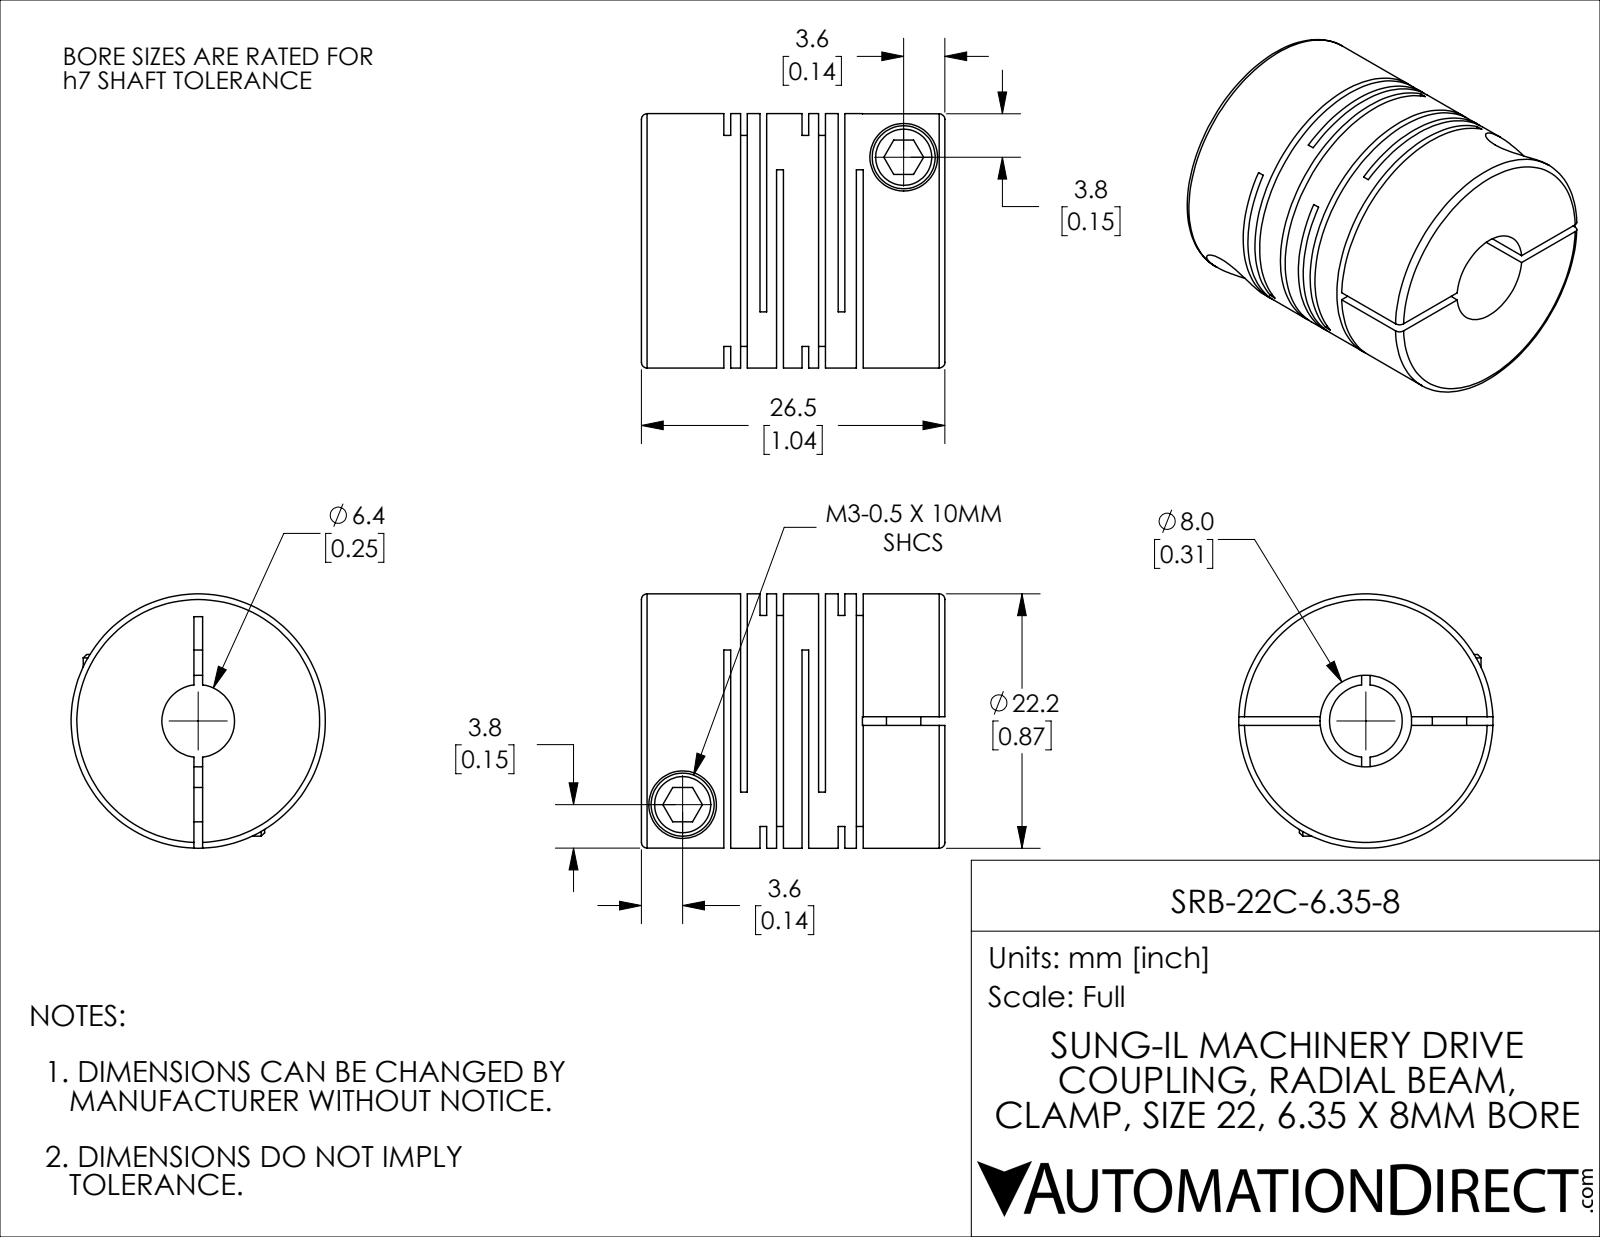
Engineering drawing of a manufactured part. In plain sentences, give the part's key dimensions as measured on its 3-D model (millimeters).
The part is named "SRB-22C-6.35-8". Its 3-D file was written by "SolidWorks 2021 (CONFIG_CONTROL_DESIGN)". It is 1 solid with 115 faces: 60 planar, 42 cylindrical and 13 other. Overall it measures 26.5 by 22.2 by 22.2 millimeters. Its volume is 7 436 cubic millimeters and its surface area 7 881 square millimeters. Round holes: 2 of diameter 3, 2 of diameter 5.9, 1 of diameter 6.35, 1 of diameter 8. Round bosses or shafts: 2 of diameter 5.5, 1 of diameter 22.2. The main face-to-face distances are 0.59, 6.82, 1.45, 3.15, 5.37, 1.7, 3.67, 2.04, 7.41, 6.23.
